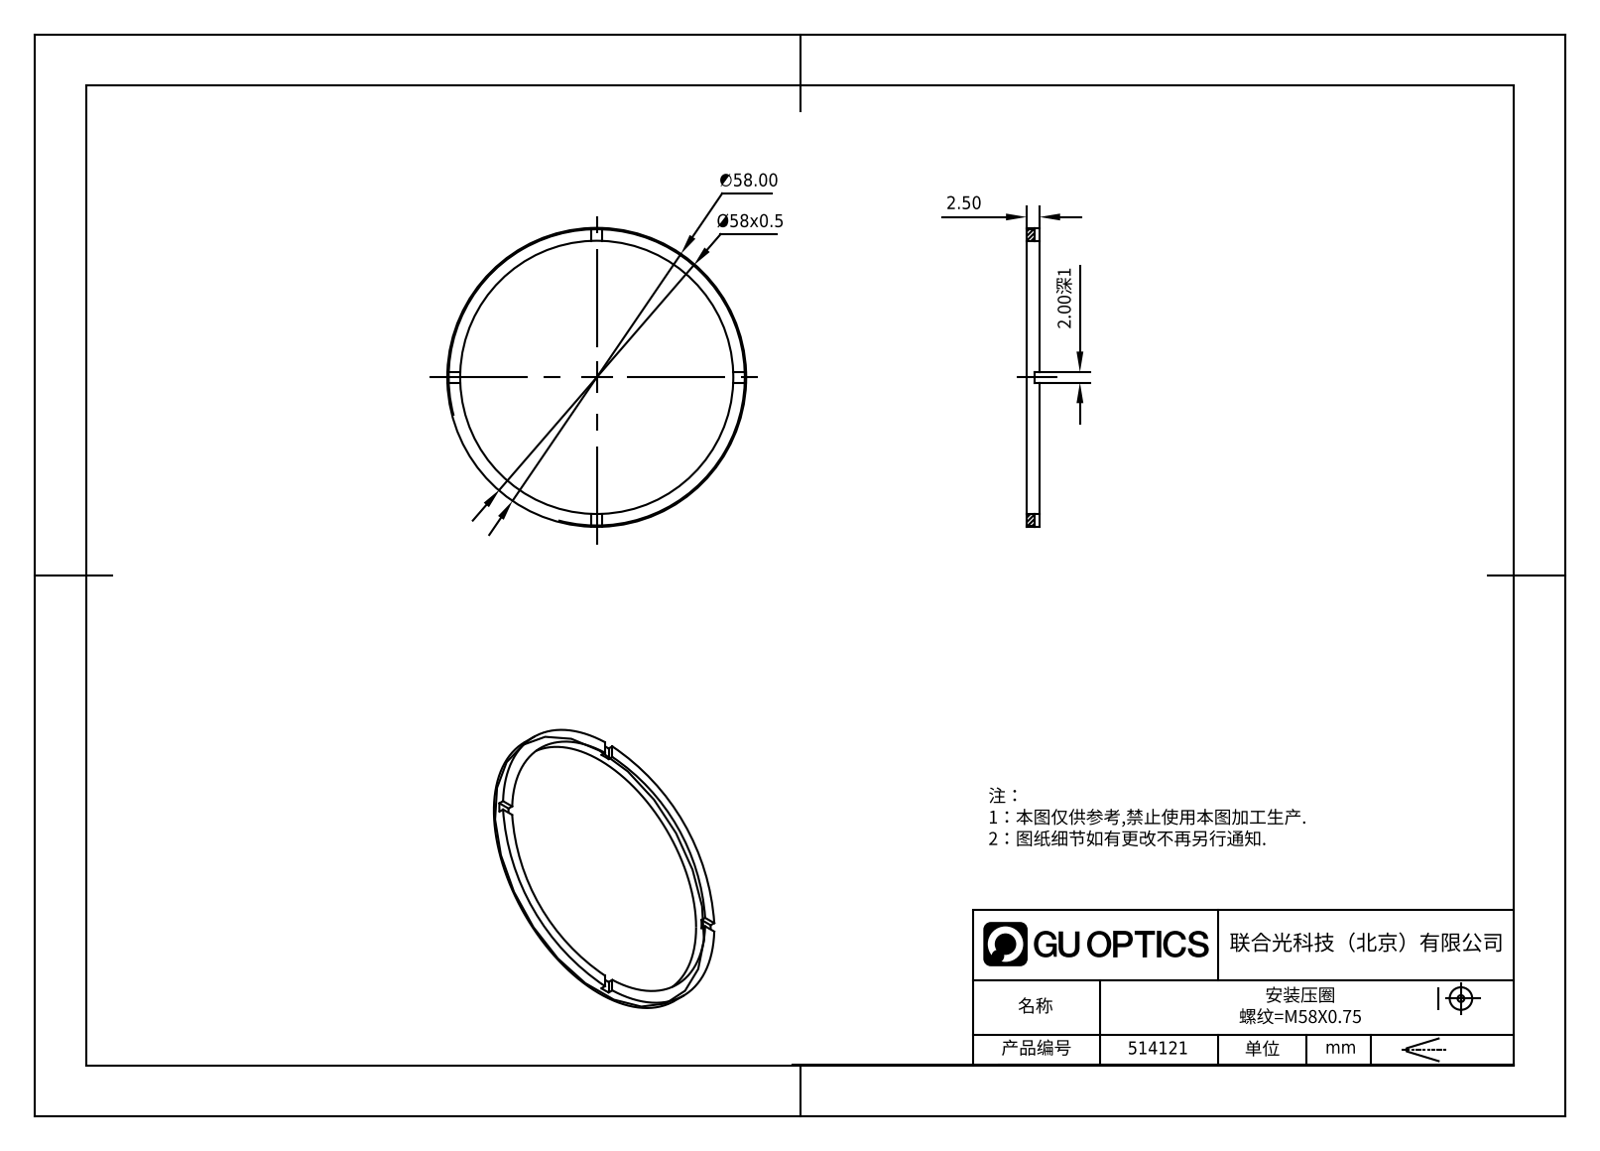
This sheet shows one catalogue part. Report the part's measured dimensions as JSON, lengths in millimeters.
{"part_name": "514121", "step_written_by": "SolidWorks 2020 (CONFIG_CONTROL_DESIGN)", "units": "millimeters", "bodies": {"solids": 1, "faces": 21, "planar": 17, "cylindrical": 4, "other": 0}, "overall_size": [58, 58, 2.5], "volume_mm3": 1070, "surface_area_mm2": 1748, "round_holes": [[53, 1]], "round_bosses_or_shafts": [[58, 1]], "face_to_face_distances": [2.5, 1.5, 1, 2]}
